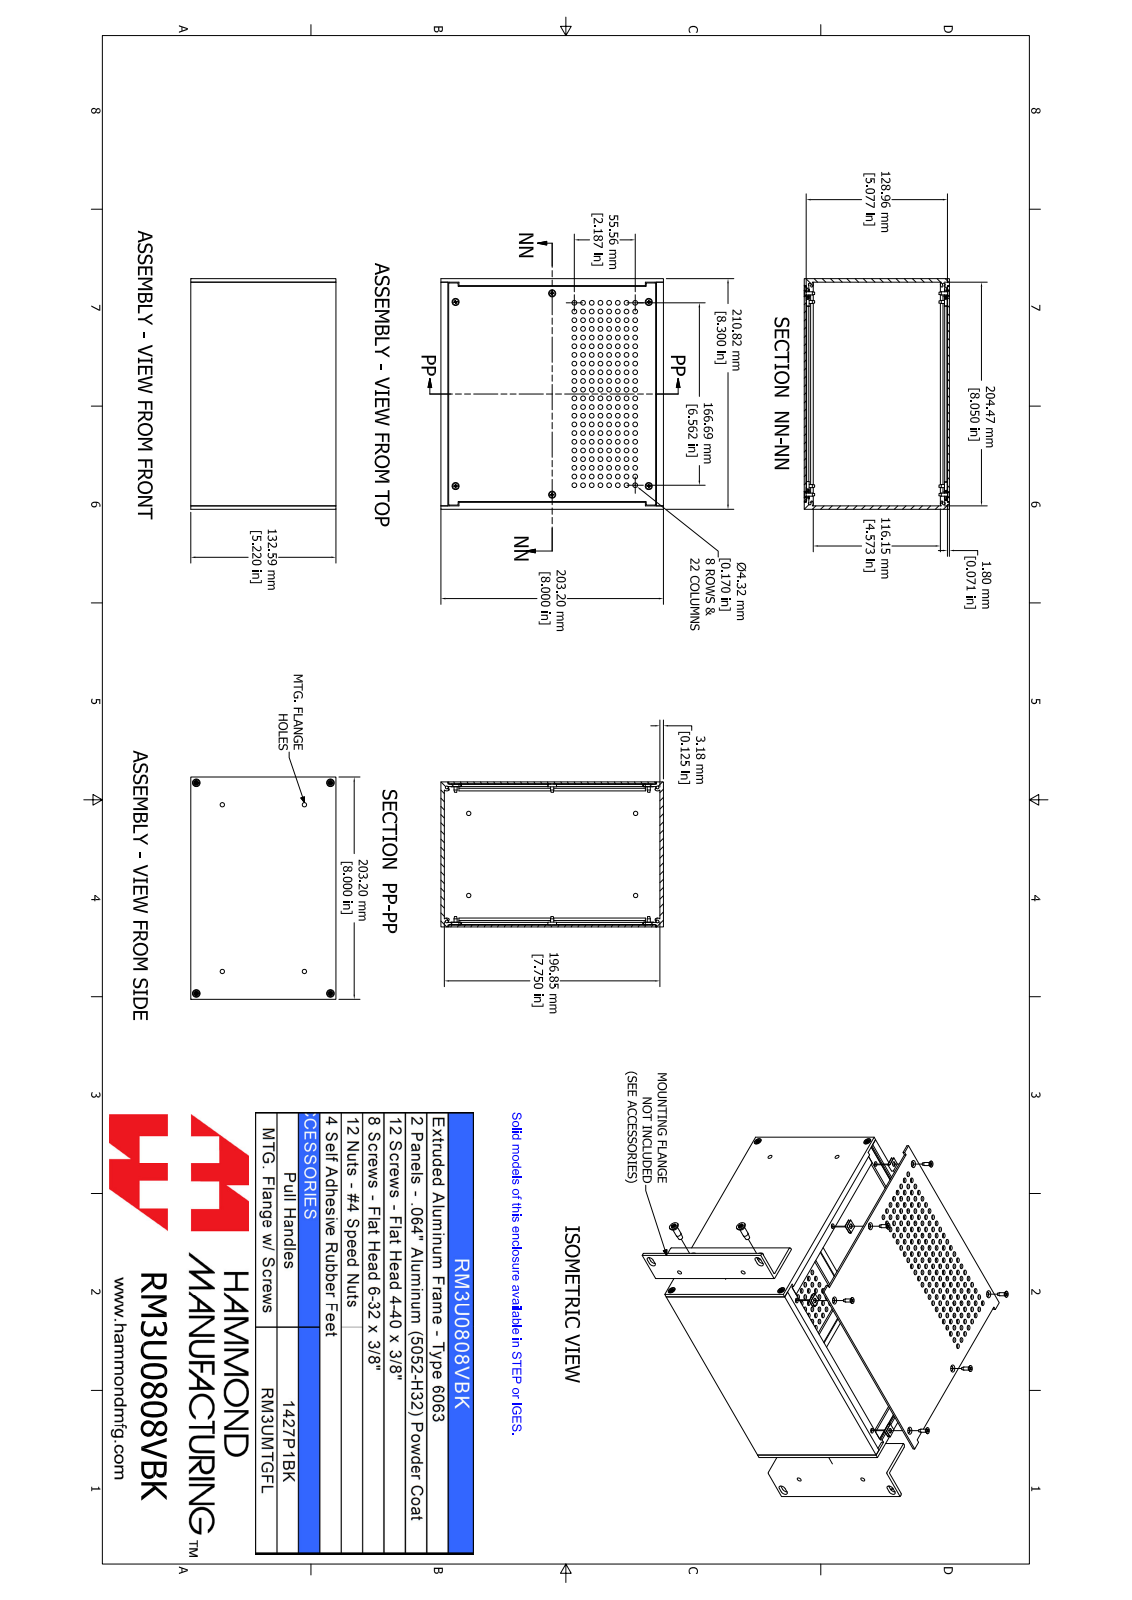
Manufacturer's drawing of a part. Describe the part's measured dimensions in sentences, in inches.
The part is named "RM3U0808VBK". Its 3-D file was written by "SolidWorks 2021 (AUTOMOTIVE_DESIGN)". It is 38 solids with 1328 faces: 468 planar, 508 cylindrical and 352 other. Overall it measures 8.3 by 8 by 5.22 inches. Its volume is 32.65 cubic inches and its surface area 671.9 square inches. Round holes: 176 of diameter 0.17, 6 of diameter 0.098, 6 of diameter 0.157, 6 of diameter 0.169, 4 of diameter 0.138, 4 of diameter 0.156. Round bosses or shafts: 6 of diameter 0.214, 6 of diameter 0.112, 4 of diameter 0.238, 4 of diameter 0.138. Partial cylindrical surfaces (rounded edges, fillets, slot ends): 12 of radius 0.039, 12 of radius 0.049, 8 of radius 0.037, 8 of radius 0.05, 8 of radius 0.125, 4 of radius 0.038. The main face-to-face distances are 0.071, 5.149, 0.125, 0.125, 5.22, 5.078, 8, 8.3, 8.05, 7.75. The hole center spacings are 0.313, 0.699, 0.442, 1.289, 0.988, 1.25, 0.937, 0.625.
